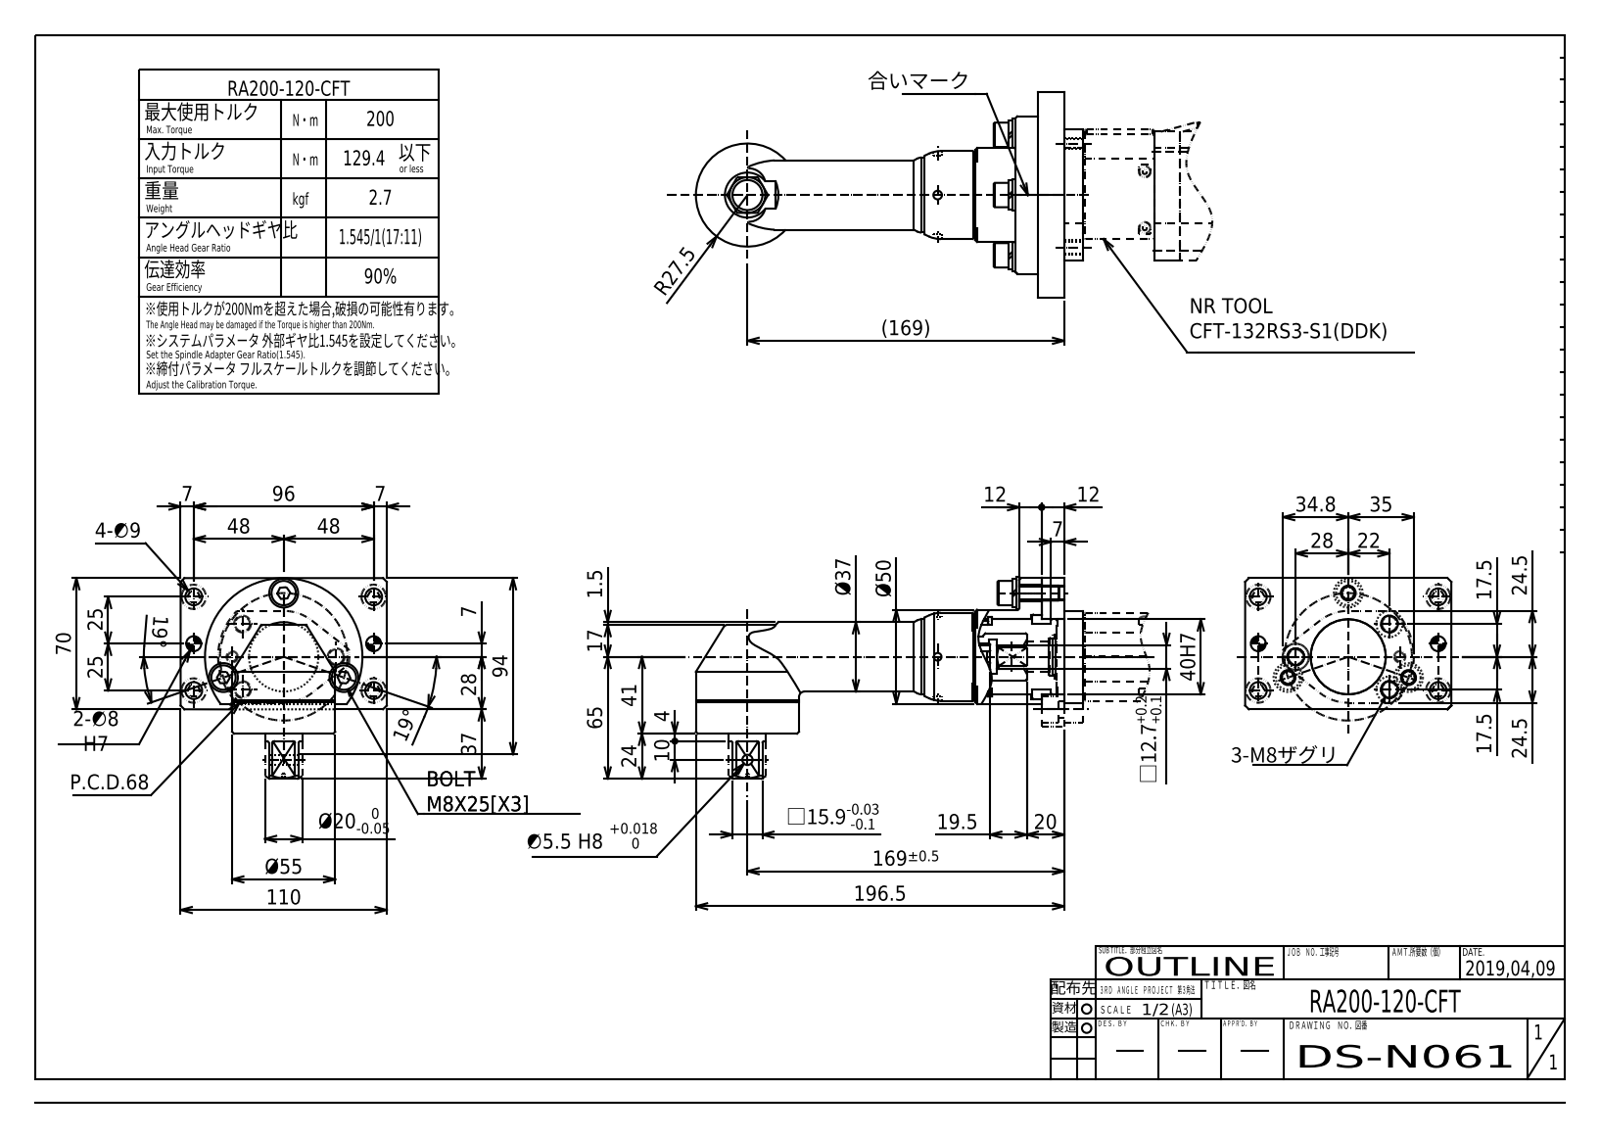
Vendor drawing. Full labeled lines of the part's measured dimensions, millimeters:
Part name (STEP PRODUCT): RA200-120-CFT(DS-N061)
STEP written by: Autodesk Inventor 2019 (AUTOMOTIVE_DESIGN)
Units: millimetres
Bodies: 1 solid, 248 faces (120 planar, 83 cylindrical, 45 other)
Overall size (bounding box): 196.5 × 110 × 107.5
Volume: 390 513 mm³ · Surface area: 69 101 mm²
Round holes (diameter × count): ⌀9 ×7, ⌀4.6 ×6, ⌀4.92 ×3, ⌀8.2 ×3, ⌀8.4 ×3, ⌀14 ×3, ⌀8 ×2, ⌀1.6 ×1, ⌀5.5 ×1, ⌀16 ×1, ⌀18 ×1, ⌀20.5 ×1
Round bosses / shafts (diameter × count): ⌀17 ×3, ⌀15.4 ×3, ⌀13 ×3, ⌀8 ×3, ⌀55 ×1, ⌀52 ×1, ⌀50 ×1, ⌀47 ×1
Partial cylindrical surfaces — rounded edges, fillets, slot ends (radius × count): R1 ×8, R4.2 ×6, R29.8 ×1, R38.2 ×1, R42 ×1
Main face-to-face distances: 12, 24, 13, 3, 70, 83, 17, 5, 16, 67
Hole centre spacings: 20, 25, 28.28, 99.2, 34, 96, 17.3, 24.04
